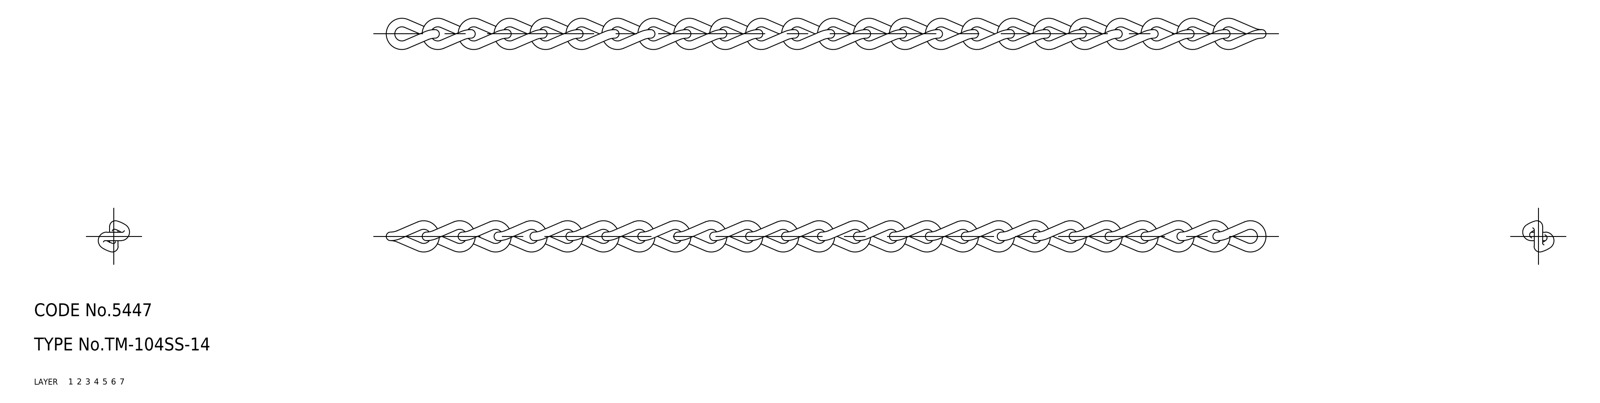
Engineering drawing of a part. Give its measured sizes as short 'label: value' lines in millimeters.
name: chain; TM_104SS_14_10088_36
written by: CADfix (AUTOMOTIVE_DESIGN)
unit: mm
bodies: 24 solids, 576 faces (0 planar, 0 cylindrical, 576 other)
size: 205.6 × 7.3 × 7.3
volume: 2 177 mm³; area: 4 348 mm²
